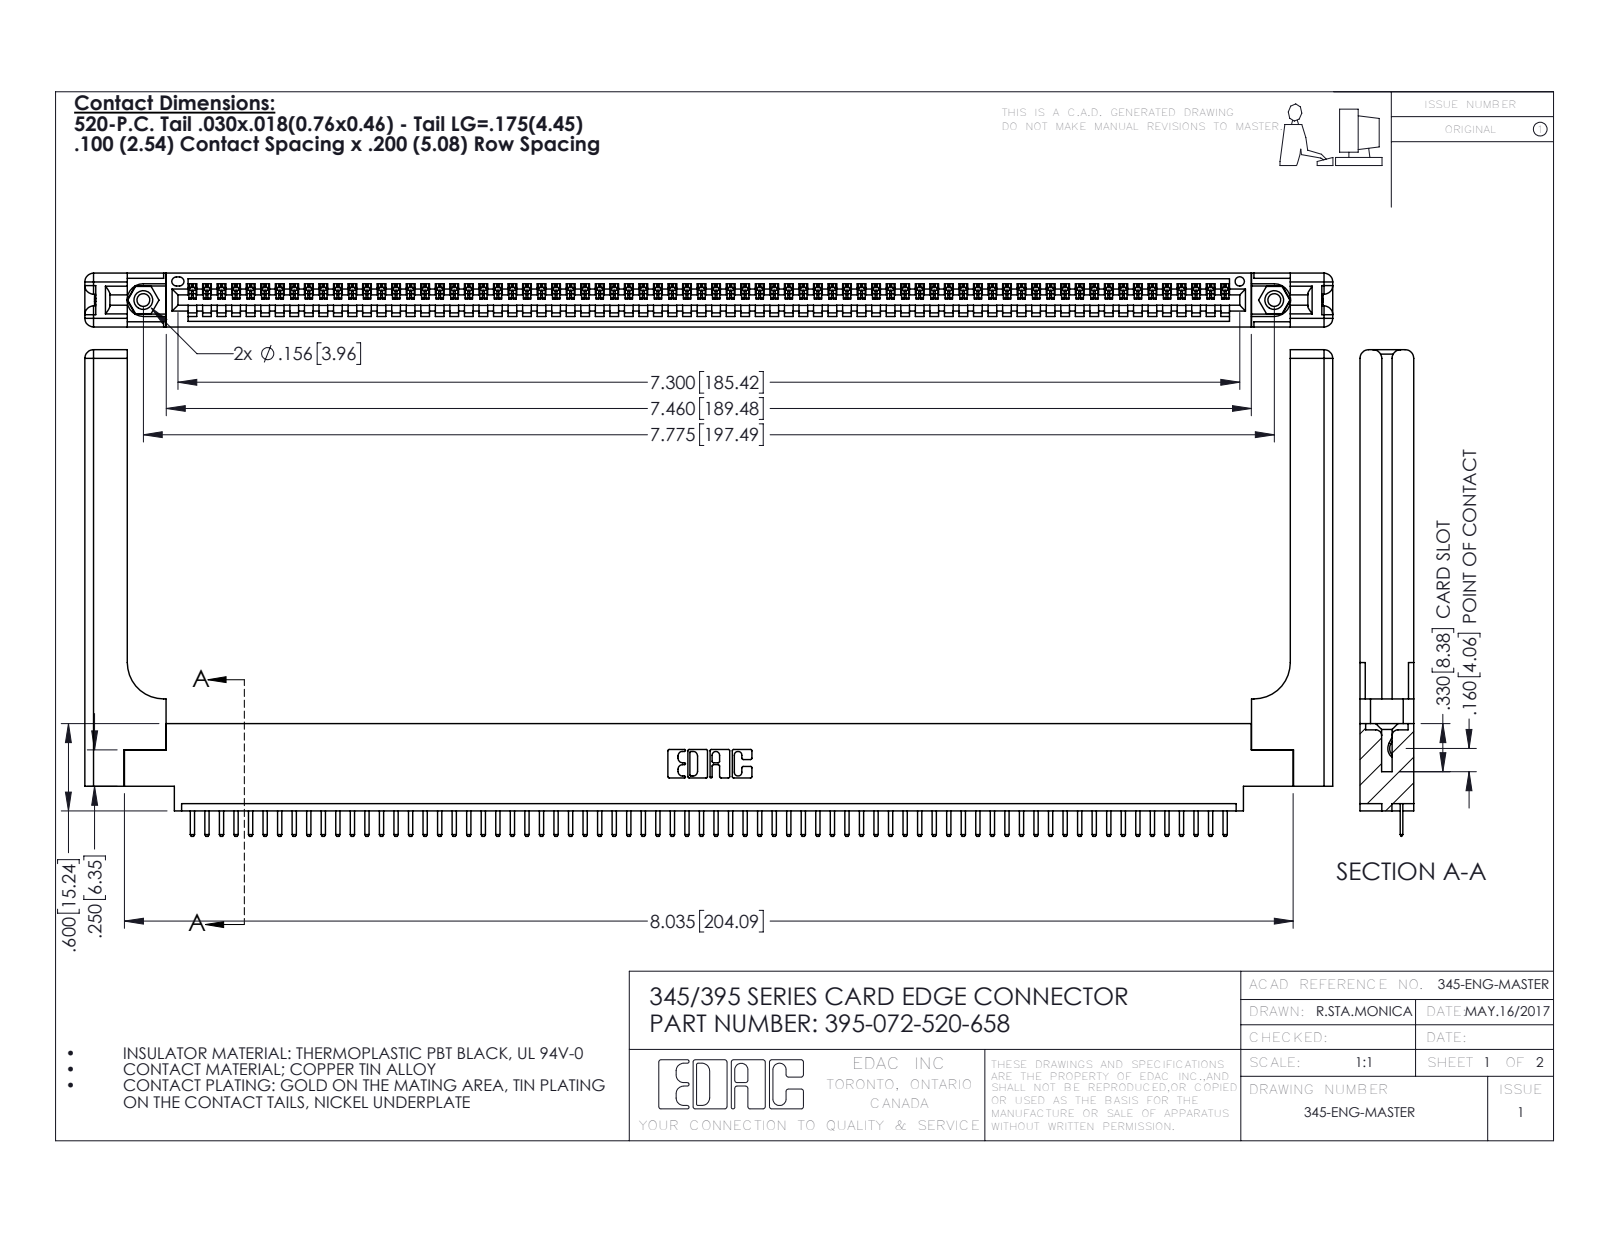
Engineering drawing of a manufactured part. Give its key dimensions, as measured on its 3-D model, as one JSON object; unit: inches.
{"part_name": "395-072-520-658; 345-220-058_345-220-058; 345-250-001_345-250-001-102; 345-292-001_345-293-120 (+1 more)", "step_written_by": "SolidWorks 2016 (CONFIG_CONTROL_DESIGN)", "units": "inches", "bodies": {"solids": 77, "faces": 4850, "planar": 3256, "cylindrical": 1534, "other": 60}, "overall_size": [8.579, 3.345, 0.37], "volume_in3": 1.777, "surface_area_in2": 50.48, "round_holes": [[0.089, 2], [0.125, 2], [0.156, 2], [0.064, 1]], "round_bosses_or_shafts": [[0.155, 2]], "partial_cylinders_radius": [[0.01, 146], [0.006, 144], [0.01, 22], [0.06, 16], [0.007, 6], [0.031, 6], [0.026, 3], [0.03, 2]], "face_to_face_distances": [0.072, 0.37, 0.298, 0.098, 0.272, 0.025, 0.2, 0.225, 0.148, 0.15], "hole_center_spacings": [0.27, 7.539, 7.775]}
